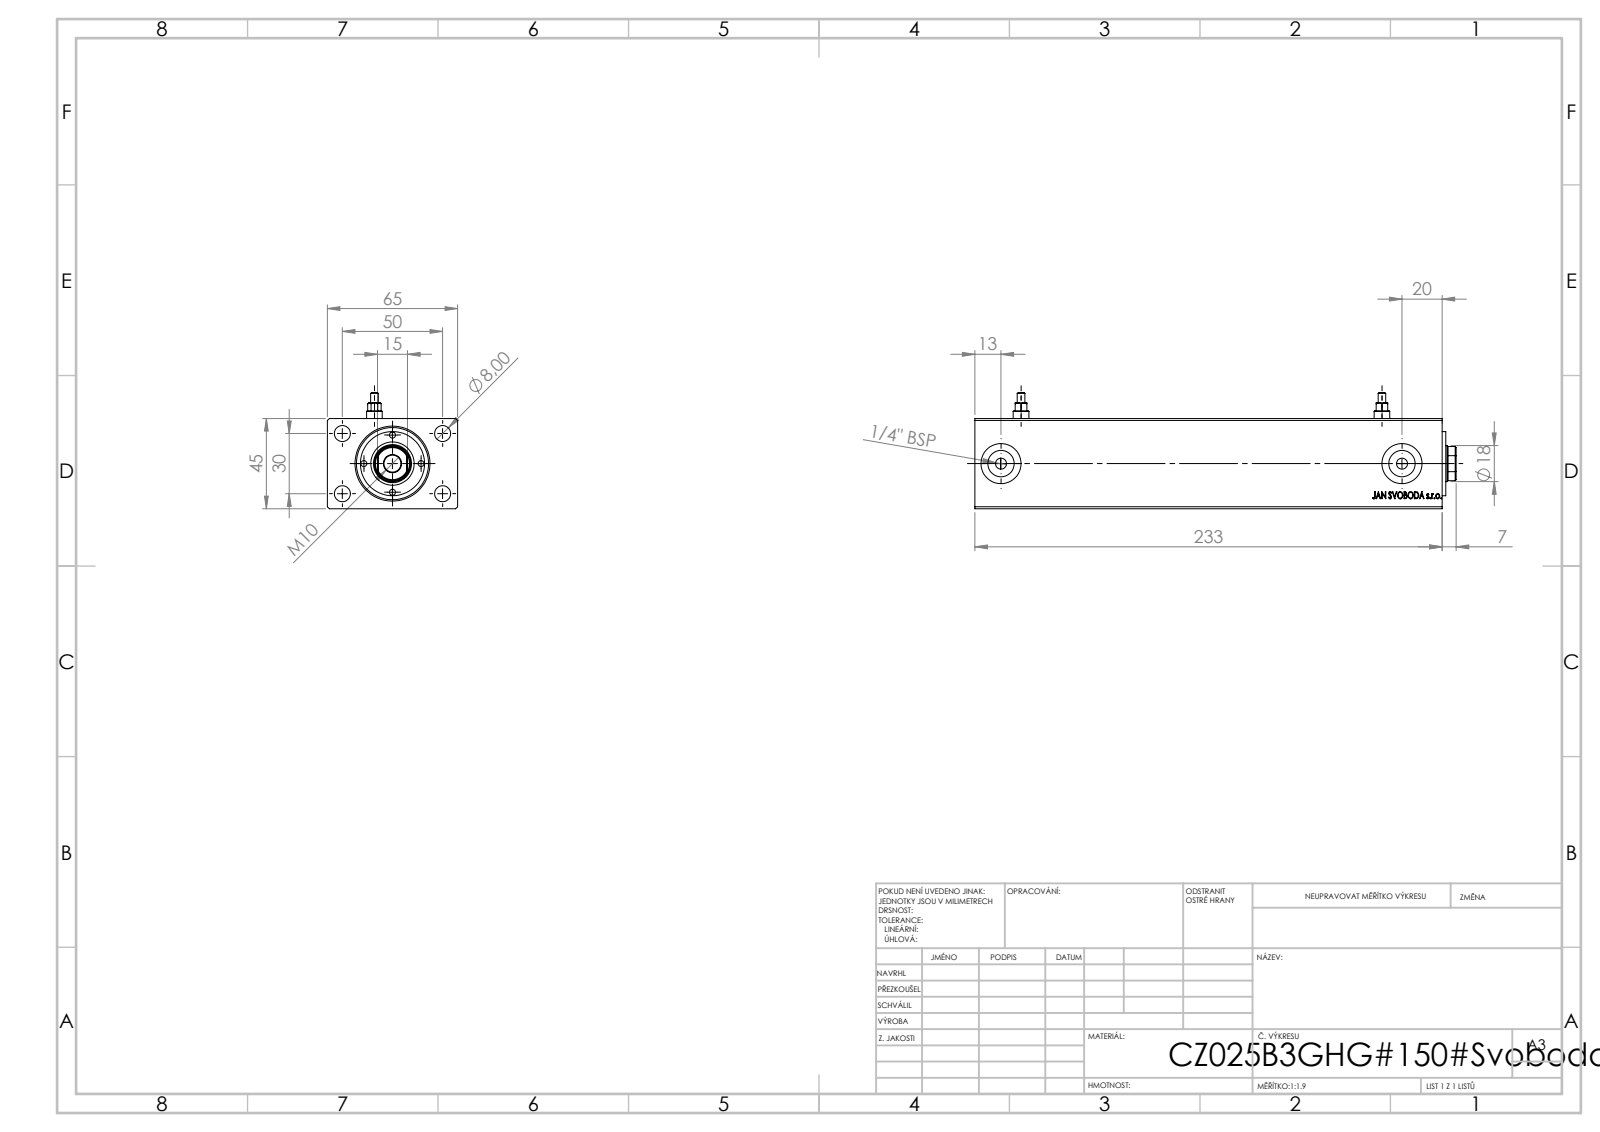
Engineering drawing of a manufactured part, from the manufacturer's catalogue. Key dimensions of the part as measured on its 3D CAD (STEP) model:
Part name (STEP PRODUCT): V500CZ_B_VC; Zatka_Cushioning3; V500CZ
STEP written by: SolidWorks 2019 (CONFIG_CONTROL_DESIGN)
Units: millimetres
Bodies: 5 solids, 933 faces (423 planar, 74 cylindrical, 436 other)
Overall size (bounding box): 240 × 65 × 58
Volume: 632 000 mm³ · Surface area: 99 532 mm²
Round holes (diameter × count): ⌀8 ×6, ⌀3 ×4, ⌀1.8 ×2, ⌀5.5 ×2, ⌀13.16 ×2, ⌀20 ×2, ⌀8.5 ×1, ⌀18 ×1, ⌀19 ×1, ⌀25 ×1, ⌀36 ×1
Round bosses / shafts (diameter × count): ⌀7.8 ×2, ⌀3.8 ×2, ⌀32 ×1
Partial cylindrical surfaces — rounded edges, fillets, slot ends (radius × count): R8.5 ×1
Main face-to-face distances: 45, 65, 233, 7, 232.8, 12.8, 220.2, 12.6, 1.8, 5.2
Hole centre spacings: 14.25, 18.45, 20.15, 25.01, 29.15, 38.48, 42.02, 28.5
